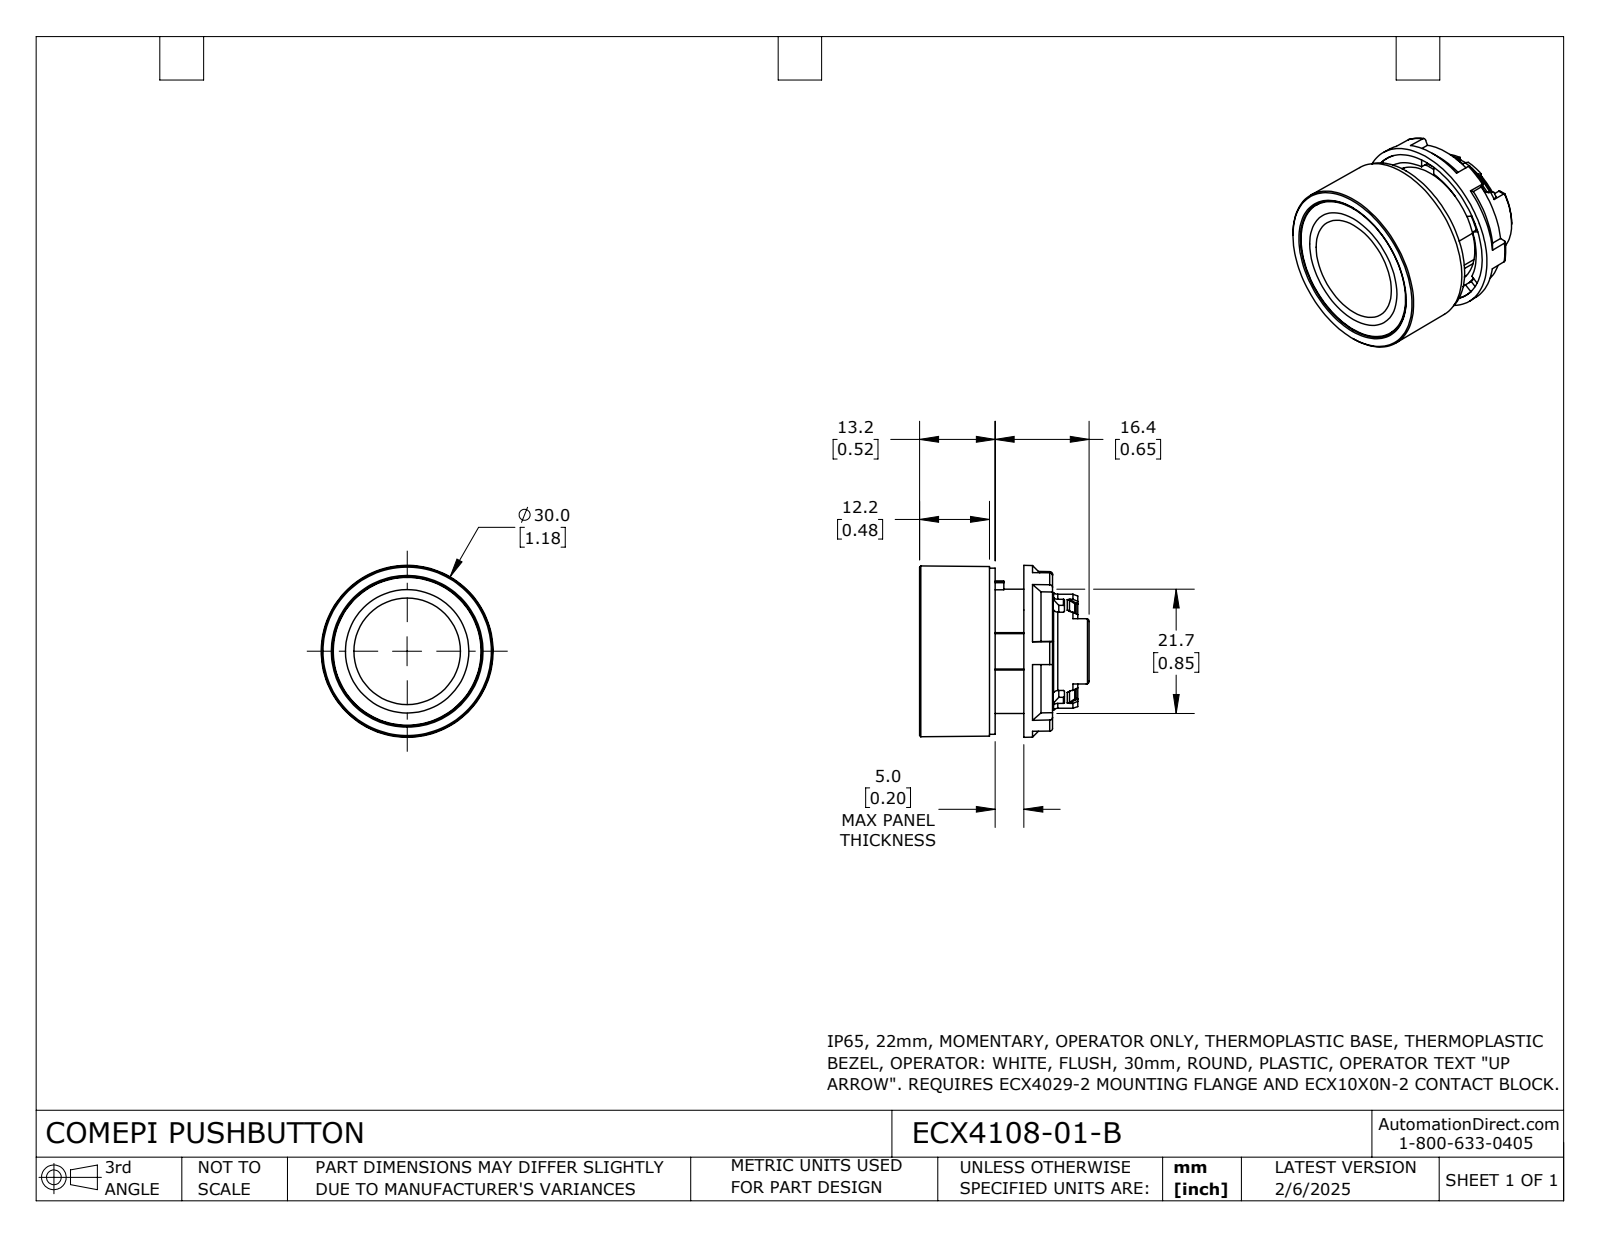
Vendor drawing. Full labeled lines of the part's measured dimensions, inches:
Part name (STEP PRODUCT): ECX4108-01-B
STEP written by: SolidWorks 2024 (CONFIG_CONTROL_DESIGN)
Units: inches
Bodies: 3 solids, 398 faces (134 planar, 111 cylindrical, 153 other)
Overall size (bounding box): 1.181 × 1.181 × 1.165
Volume: 0.472 in³ · Surface area: 16.55 in²
Round holes (diameter × count): ⌀0.531 ×1, ⌀0.713 ×1, ⌀0.866 ×1
Round bosses / shafts (diameter × count): ⌀1.142 ×1, ⌀1.016 ×1, ⌀0.965 ×1, ⌀0.854 ×1, ⌀0.807 ×1, ⌀0.787 ×1, ⌀0.748 ×1, ⌀0.728 ×1
Partial cylindrical surfaces — rounded edges, fillets, slot ends (radius × count): R0.008 ×24, R0.02 ×8, R0.01 ×2, R0.293 ×1, R0.344 ×1, R0.348 ×1, R0.366 ×1
Main face-to-face distances: 0.409, 0.039, 0.433, 0.472, 0.236, 0.394, 0.197, 0.449, 0.512, 0.217
